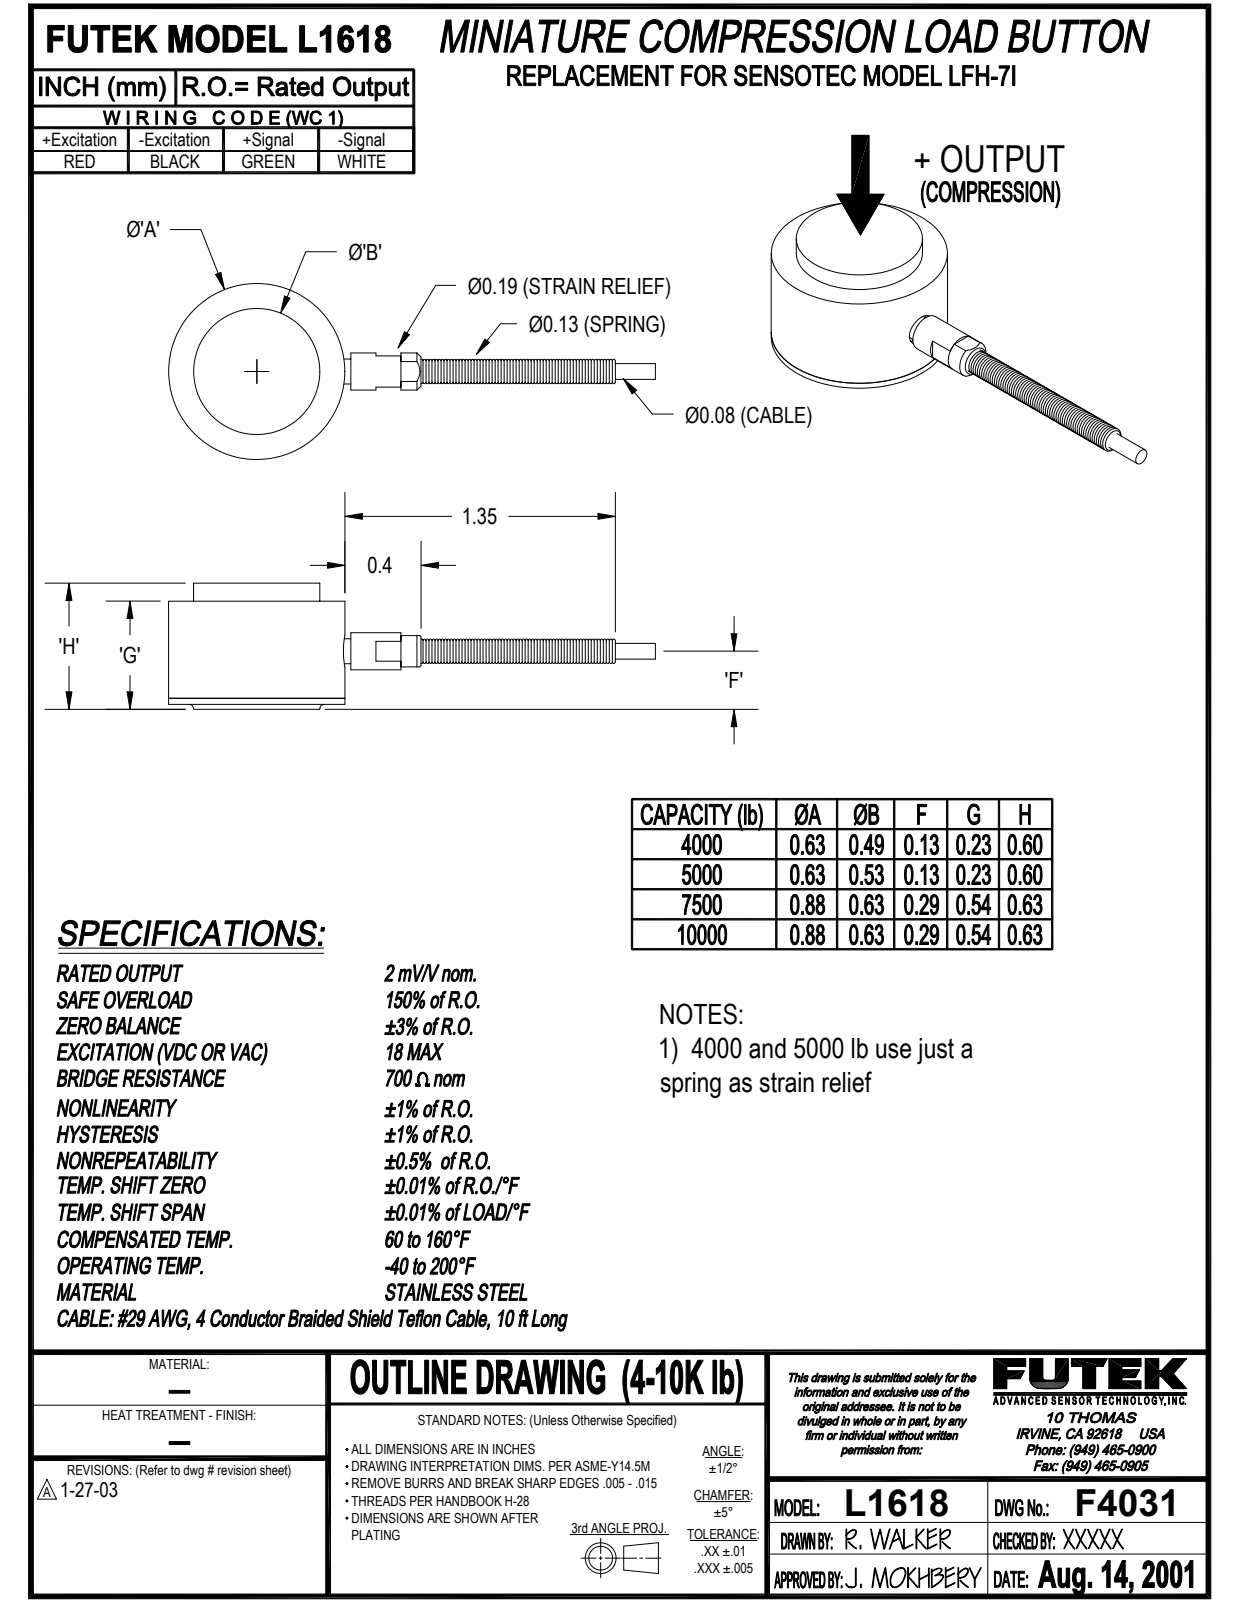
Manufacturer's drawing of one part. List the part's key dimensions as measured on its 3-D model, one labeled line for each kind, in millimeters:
Part name (STEP PRODUCT): LCA345; FM1635; $F2652; ~PART1 (+5 more)
STEP written by: Autodesk Inventor 2008 (AUTOMOTIVE_DESIGN)
Units: millimetres
Bodies: 7 solids, 153 faces (47 planar, 27 cylindrical, 79 other)
Overall size (bounding box): 53.8 × 16 × 15.2
Volume: 2 200 mm³ · Surface area: 3 070 mm²
Round holes (diameter × count): ⌀1.6 ×1, ⌀2 ×1, ⌀2.1 ×1, ⌀2.7 ×1, ⌀3 ×1, ⌀3 ×1, ⌀3.2 ×1, ⌀10.9 ×1, ⌀11.4 ×1, ⌀11.8 ×1
Round bosses / shafts (diameter × count): ⌀16 ×1, ⌀12.4 ×1, ⌀11.6 ×1, ⌀11.3 ×1, ⌀10.7 ×1, ⌀4.7 ×1, ⌀3.5 ×1, ⌀2.8 ×1
Partial cylindrical surfaces — rounded edges, fillets, slot ends (radius × count): R1.2 ×1
Main face-to-face distances: 0.8, 4.8, 5.6, 1, 5.8, 2.5, 2.8, 1.8, 3, 6.4
Hole centre spacings: 4.4
